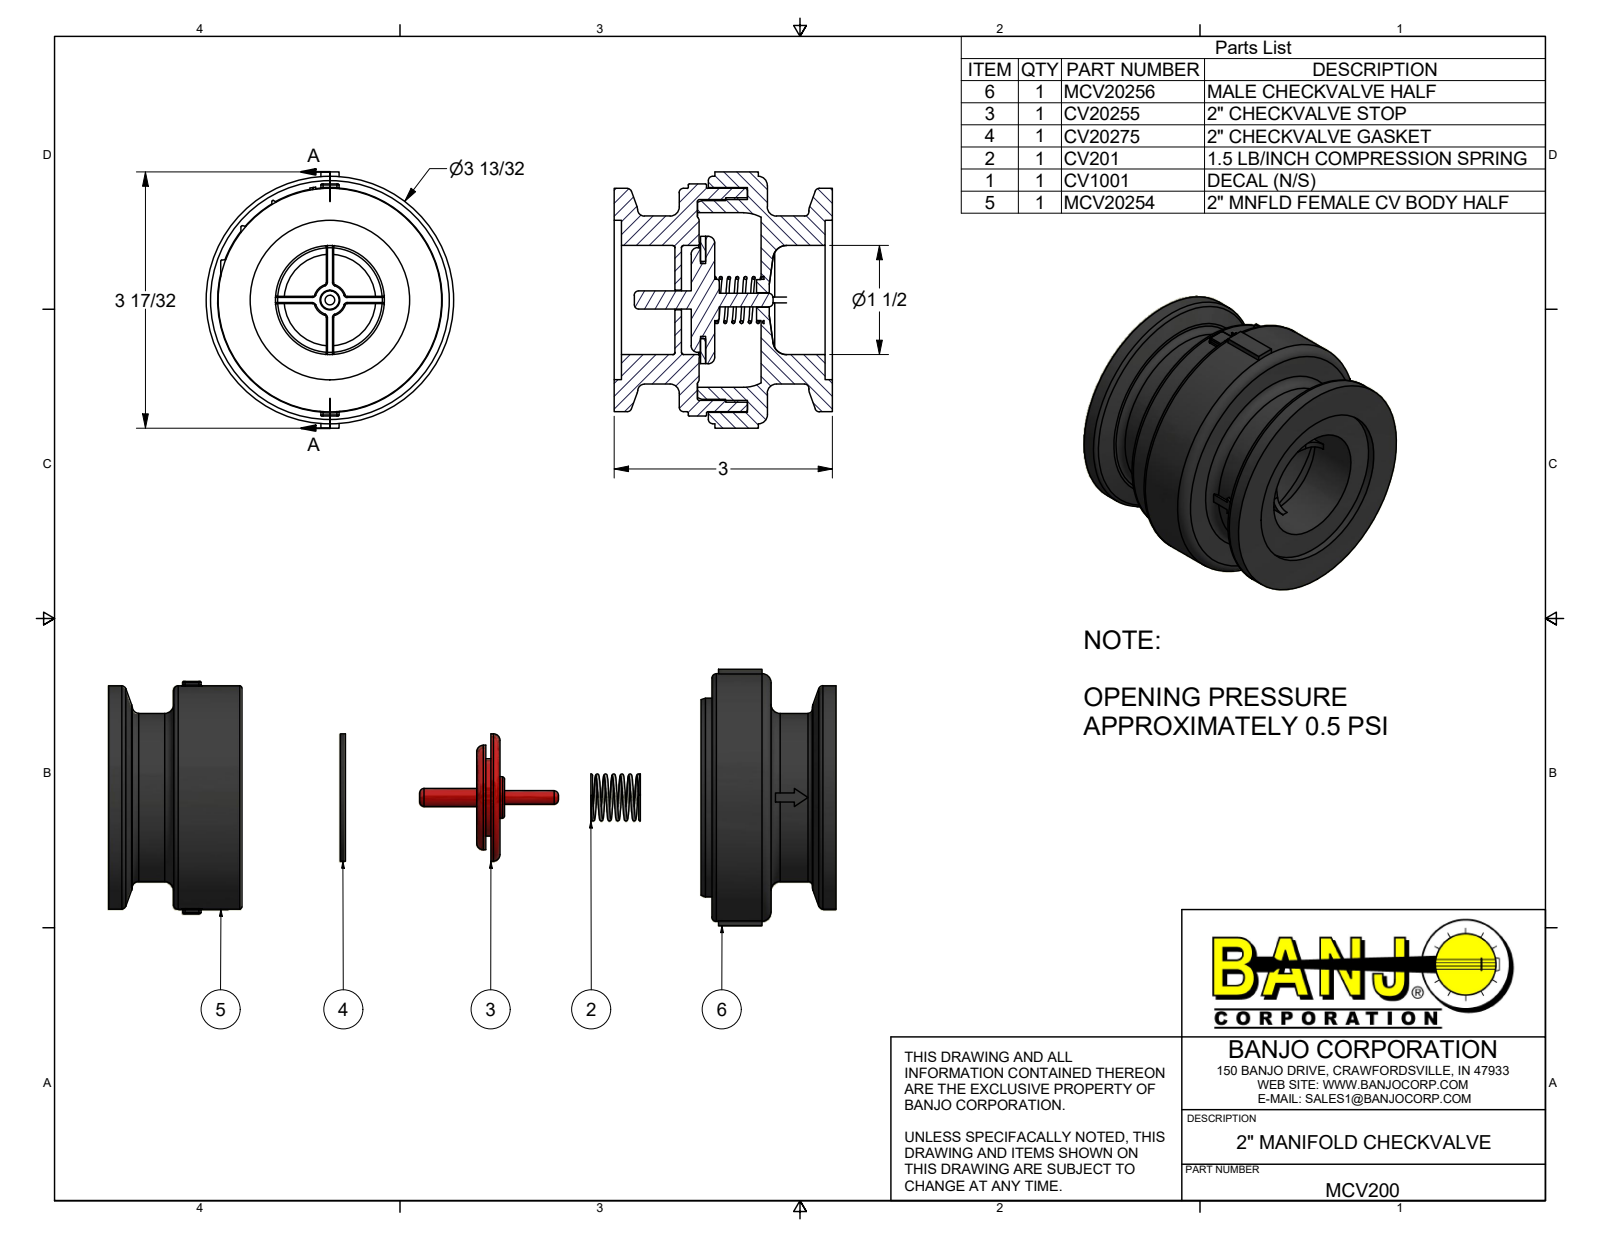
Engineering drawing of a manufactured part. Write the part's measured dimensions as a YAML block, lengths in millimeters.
part_name: "MCV200; MCV20254; MCV20254X; MCV20256 (+3 more)"
step_written_by: "Autodesk Inventor 2017 (AUTOMOTIVE_DESIGN)"
units: millimeters
bodies: {solids: 5, faces: 332, planar: 114, cylindrical: 93, other: 125}
overall_size: [89.46, 86.41, 76.22]
volume: 198873
surface_area: 76062
round_holes:
  - {diameter: 5.08, count: 1}
  - {diameter: 6.86, count: 1}
  - {diameter: 25.4, count: 1}
  - {diameter: 38.1, count: 1}
  - {diameter: 55.63, count: 1}
  - {diameter: 60.96, count: 1}
  - {diameter: 70.1, count: 1}
  - {diameter: 78.49, count: 1}
round_bosses_or_shafts:
  - {diameter: 86.41, count: 1}
  - {diameter: 77.98, count: 1}
  - {diameter: 71.37, count: 1}
  - {diameter: 69.34, count: 1}
  - {diameter: 58.67, count: 1}
  - {diameter: 44.45, count: 1}
  - {diameter: 36.51, count: 1}
  - {diameter: 26.99, count: 1}
partial_cylinders:
  - {radius: 0.38, count: 31}
  - {radius: 0.76, count: 12}
  - {radius: 5.56, count: 1}
  - {radius: 5.59, count: 1}
  - {radius: 7.14, count: 1}
  - {radius: 39.75, count: 1}
face_to_face_distances: [2.54, 73.68, 53.52, 76.22, 20.16, 31.91, 44.31, 21.61, 22.7, 46.53]
